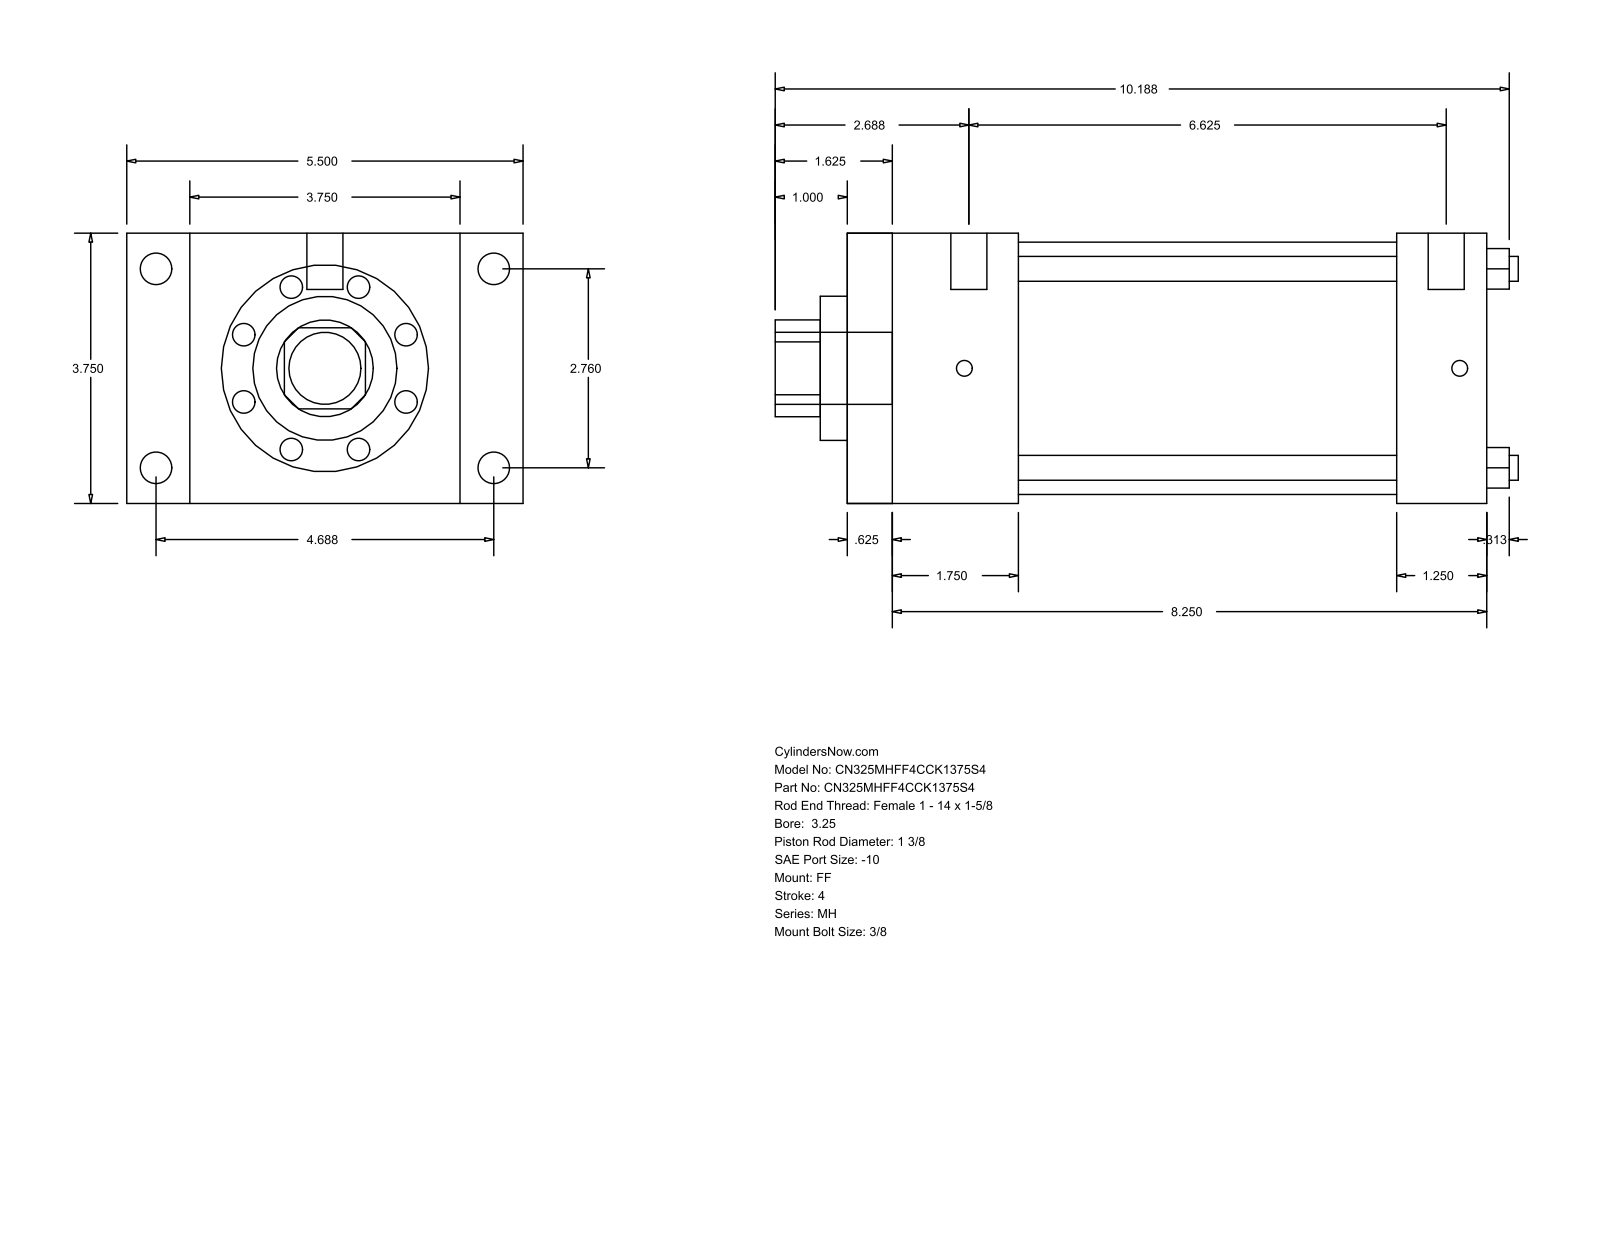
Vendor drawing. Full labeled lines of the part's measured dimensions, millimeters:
Part name (STEP PRODUCT): MH_FF__0325_1.375
STEP written by: GSSL Pune (CONFIG_CONTROL_DESIGN)
Units: millimetres
Bodies: 0 solids, 92 faces (64 planar, 28 cylindrical, 0 other)
Overall size (bounding box): 261.94 × 139.7 × 95.25
Round holes (diameter × count): ⌀8.76 ×4, ⌀34.92 ×1, ⌀50.8 ×1, ⌀88.9 ×1
Round bosses / shafts (diameter × count): ⌀11.13 ×4, ⌀5.56 ×4, ⌀12.7 ×2, ⌀25.4 ×1
Partial cylindrical surfaces — rounded edges, fillets, slot ends (radius × count): R17.06 ×1
Main face-to-face distances: 95.24, 225.42, 15.87, 209.55, 22.23, 117.47, 193.67, 177.8, 31.75, 60.32
Hole centre spacings: 49.57, 70.1, 99.14
